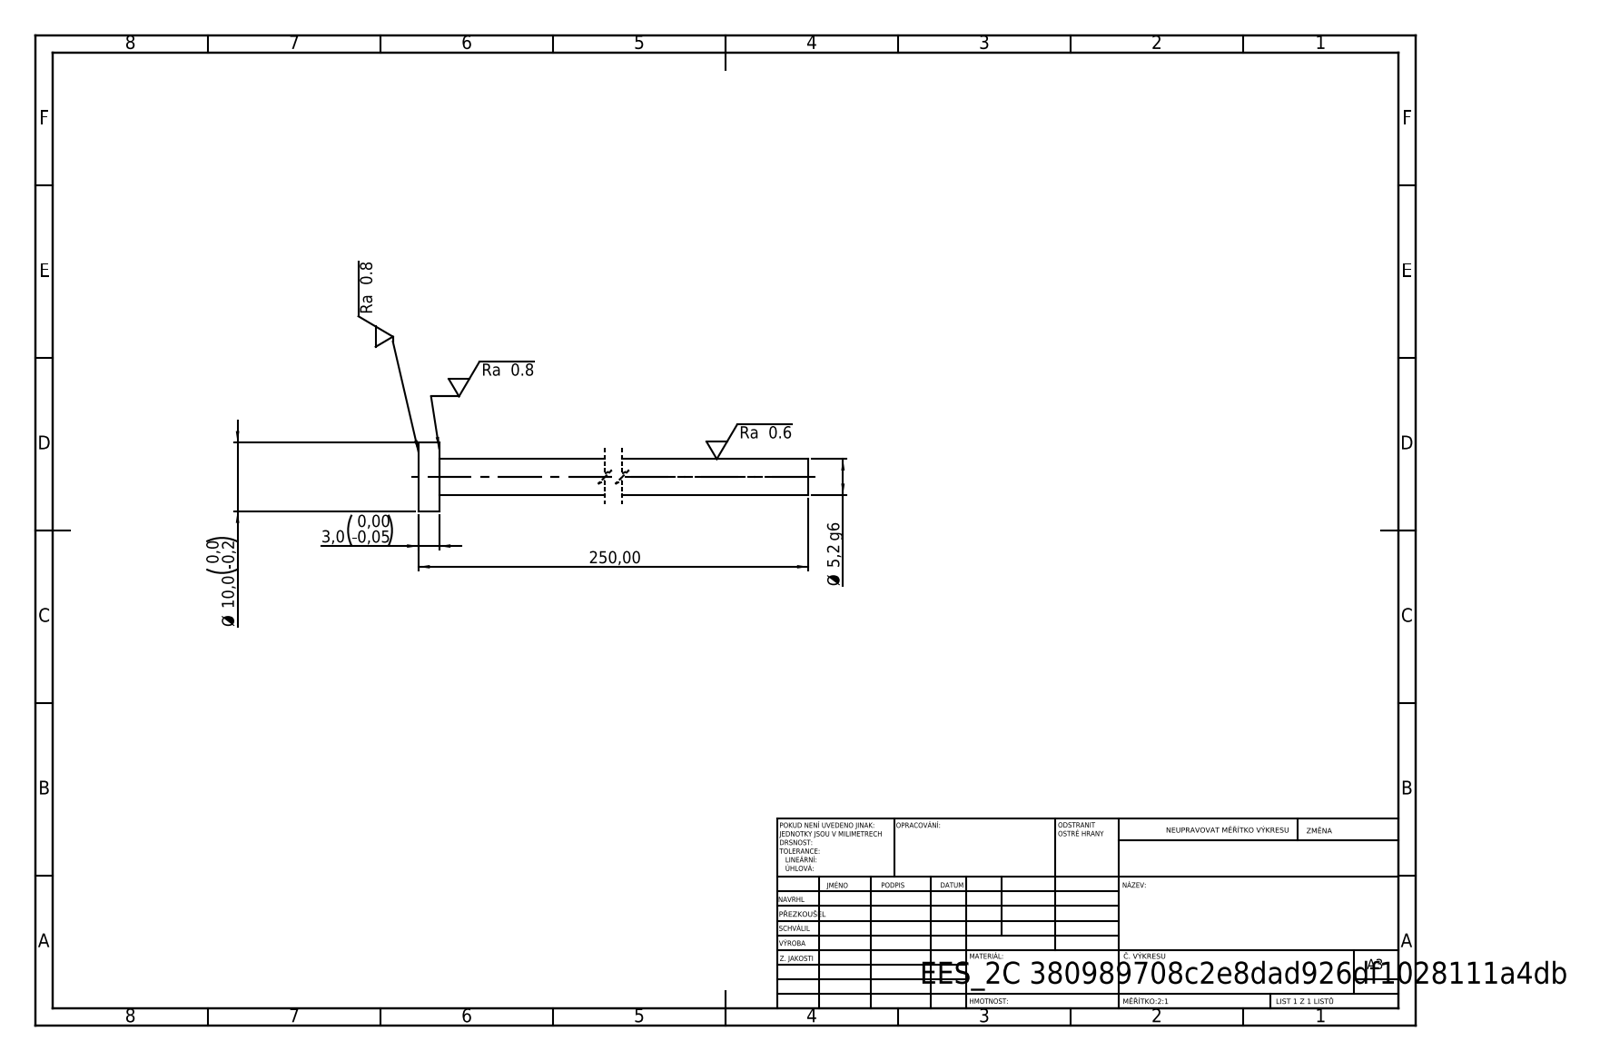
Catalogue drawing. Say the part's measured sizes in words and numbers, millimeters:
Its 3-D file was written by "SolidWorks 2019 (CONFIG_CONTROL_DESIGN)". It is 1 solid with 7 faces: 3 planar, 4 cylindrical and 0 other. Overall it measures 250 by 10 by 10 millimeters. Its volume is 5 481 cubic millimeters and its surface area 4 286 square millimeters. Round bosses or shafts: 1 of diameter 10, 1 of diameter 5.2. The main face-to-face distances are 3, 250, 247.
